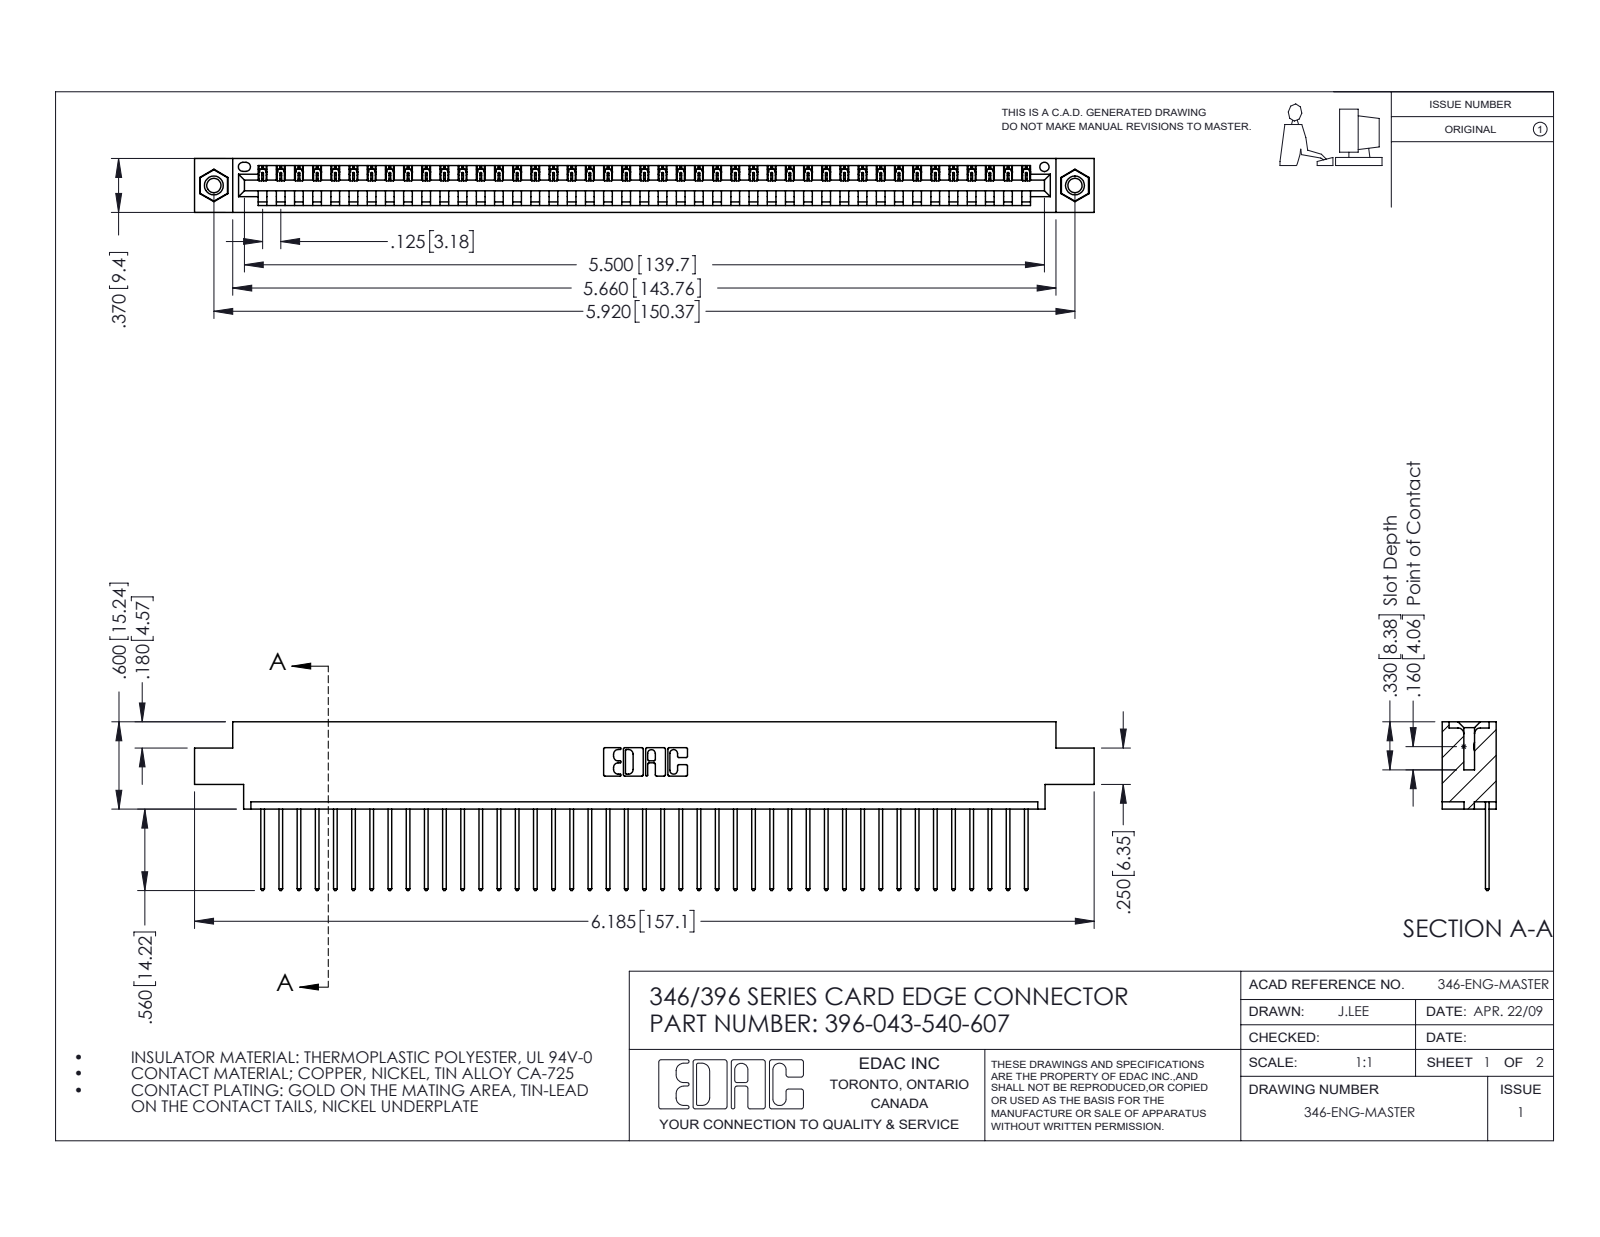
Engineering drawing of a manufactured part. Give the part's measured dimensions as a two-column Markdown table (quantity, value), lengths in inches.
| quantity | value |
| --- | --- |
| part name | 346 Part_0.170 Offset - 0.156 Dia-TI; 345-292-001_345-293-140; 345-250-001_345-250-005-103; 396-043-540-607 |
| STEP written by | SolidWorks 2016 (CONFIG_CONTROL_DESIGN) |
| units | inches |
| bodies | 46 solids, 2680 faces (1832 planar, 832 cylindrical, 16 other) |
| overall size | 6.185 × 1.16 × 0.37 |
| volume | 0.911 in³ |
| surface area | 29.91 in² |
| round holes (diameter × count) | 0.098 × 2, 0.125 × 2, 0.156 × 2, 0.064 × 1 |
| round bosses / shafts (diameter × count) | 0.155 × 2 |
| partial cylindrical surfaces (radius × count) | 0.006 × 86, 0.01 × 86, 0.01 × 22, 0.007 × 6, 0.031 × 6, 0.026 × 3, 0.031 × 2, 0.04 × 2 |
| main face-to-face distances | 0.048, 0.322, 0.37, 0.25, 0.072, 0.298, 0.025, 0.222, 0.148, 0.1 |
| hole center spacings | 0.246, 5.711, 5.92 |
